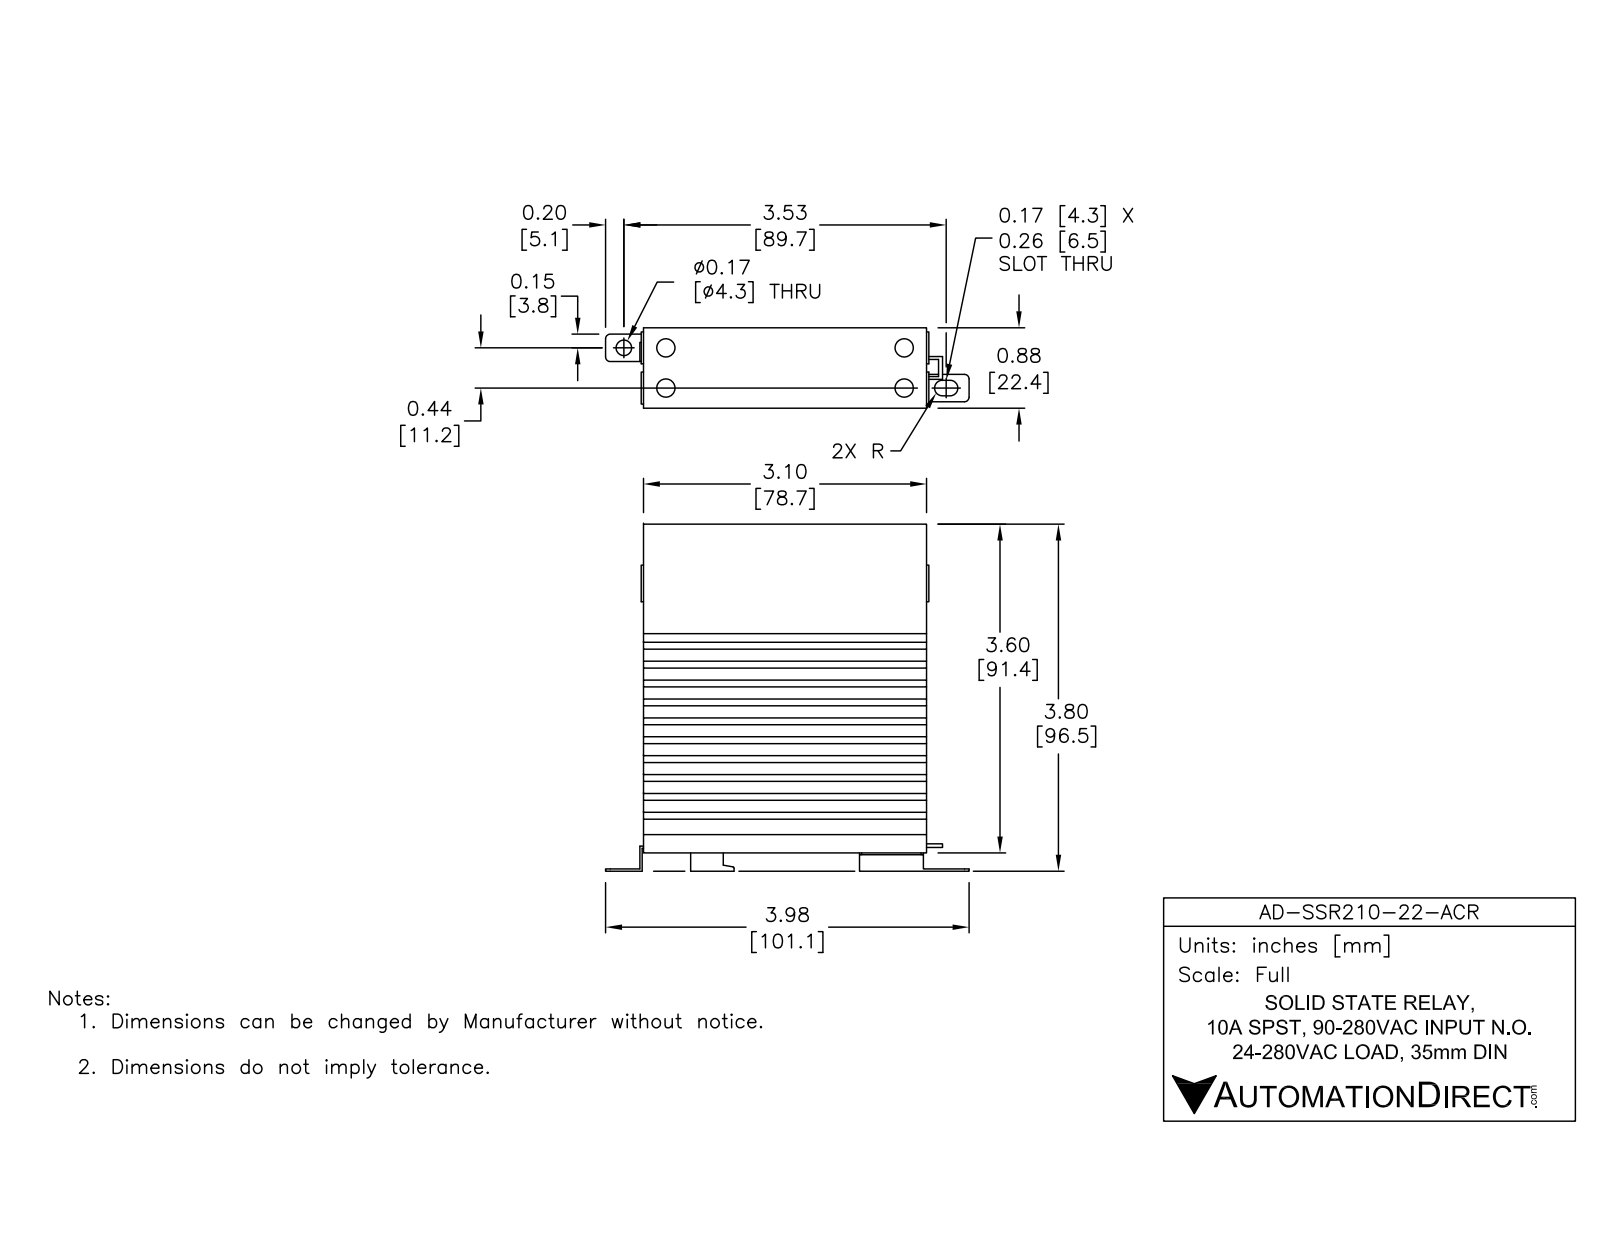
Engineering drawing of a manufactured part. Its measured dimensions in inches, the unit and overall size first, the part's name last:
Units: inches
Overall size (bounding box): 3.98 × 3.8 × 0.88
Round holes (diameter × count): ⌀0.2 ×4, ⌀0.17 ×1
Partial cylindrical surfaces — rounded edges, fillets, slot ends (radius × count): R0.05 ×6, R0.085 ×2, R0.015 ×1
Main face-to-face distances: 0.62, 0.207, 0.827, 0.414, 0.132, 0.489, 0.339, 0.413, 0.075, 0.207
Hole centre spacings: 0.44, 2.61, 2.647, 0.46, 0.637, 3.07, 3.102
Volume: 7.136 in³ · Surface area: 74.91 in²
Bodies: 1 solid, 215 faces (195 planar, 20 cylindrical, 0 other)
Part name (STEP PRODUCT): AD-SSR210-22-ACR
STEP written by: SolidWorks 2014 (AUTOMOTIVE_DESIGN)
